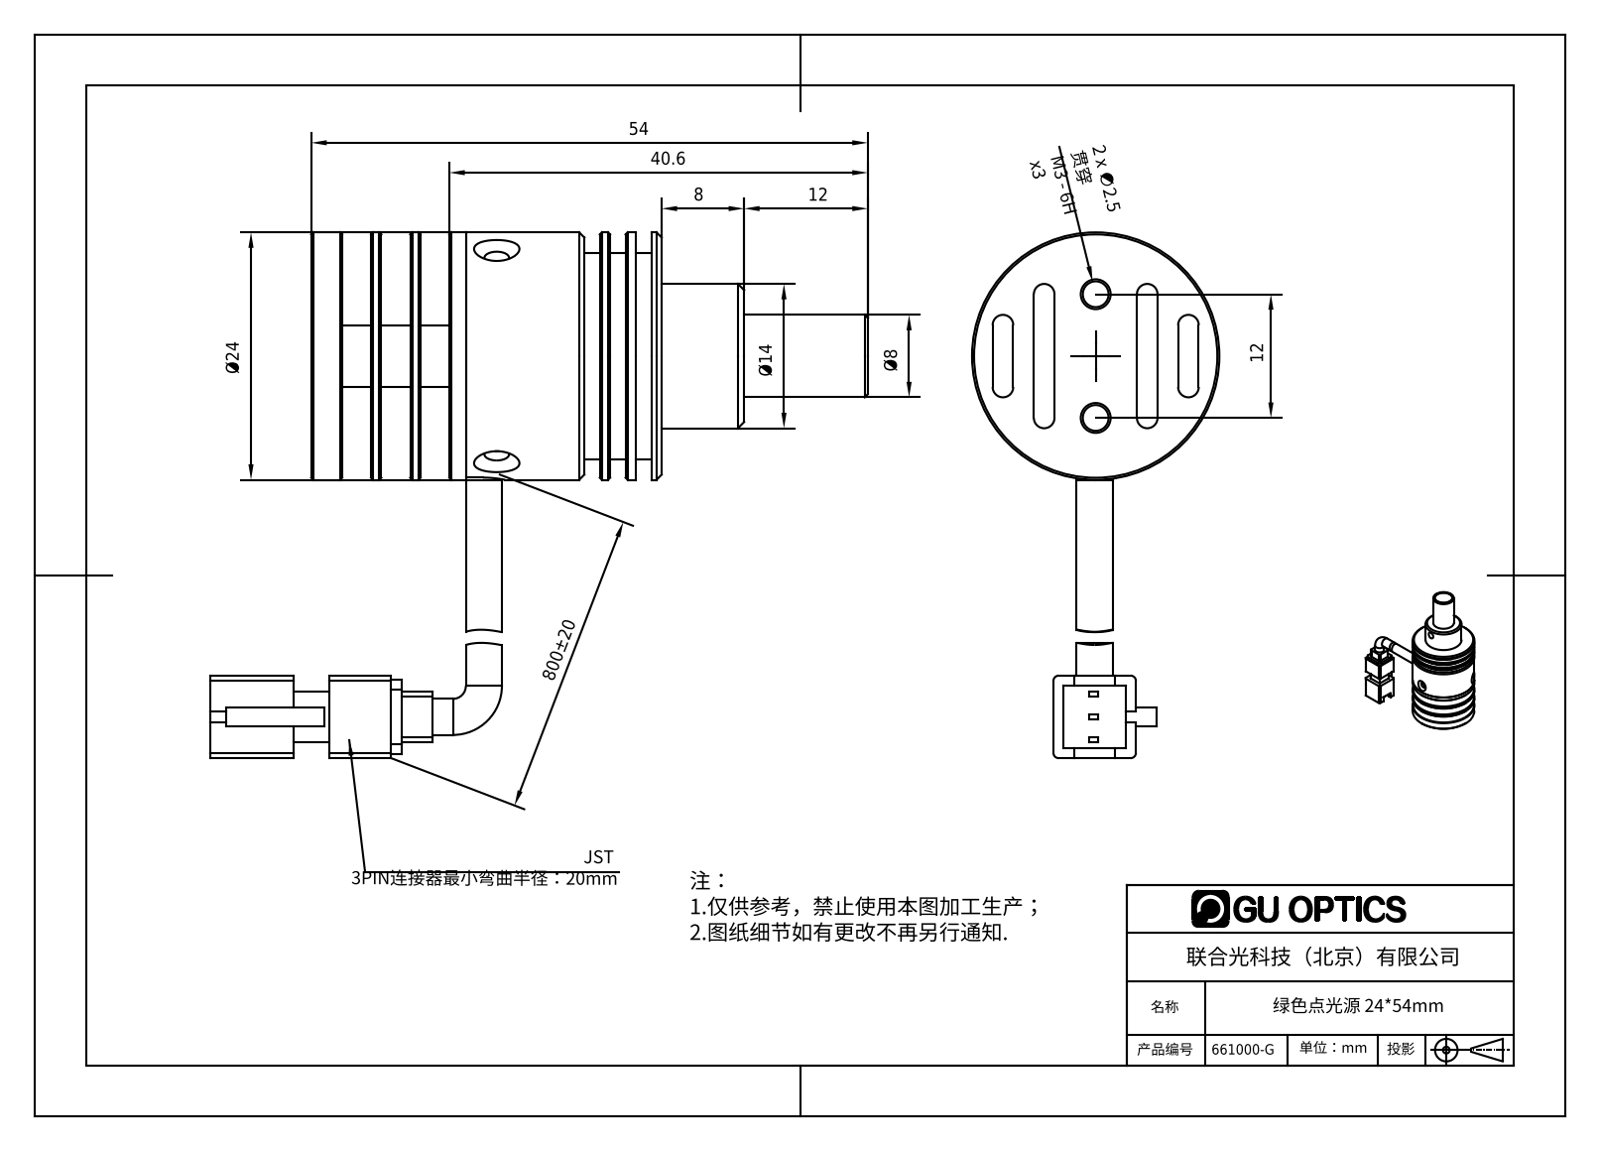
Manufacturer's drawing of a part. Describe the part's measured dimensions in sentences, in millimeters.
The part is named "661000-G". Its 3-D file was written by "SolidWorks 2016 (AUTOMOTIVE_DESIGN)". It is 10 solids with 387 faces: 153 planar, 160 cylindrical and 74 other. Overall it measures 63.75 by 51 by 24 millimeters. Its volume is 11 337 cubic millimeters and its surface area 13 807 square millimeters. Round holes: 7 of diameter 1.6, 3 of diameter 2, 3 of diameter 2.4, 3 of diameter 2.5, 2 of diameter 2.2, 1 of diameter 6.21, 1 of diameter 6.8, 1 of diameter 12, 1 of diameter 15.8, 1 of diameter 16.8, 1 of diameter 19.1, 1 of diameter 20.1. Round bosses or shafts: 2 of diameter 3.5, 1 of diameter 24, 1 of diameter 20, 1 of diameter 17, 1 of diameter 15.6, 1 of diameter 14.4, 1 of diameter 14, 1 of diameter 13.78. Partial cylindrical surfaces (rounded edges, fillets, slot ends): 12 of radius 1, 8 of radius 0.5, 3 of radius 1.5, 1 of radius 1.65. The main face-to-face distances are 3.8, 1, 6.6, 2.8, 1.5, 7.6, 5, 10.4, 6.5, 2.5. The hole center spacings are 6, 8.49, 4.59, 4.6, 11.09, 12.01, 6.01, 11.08.
